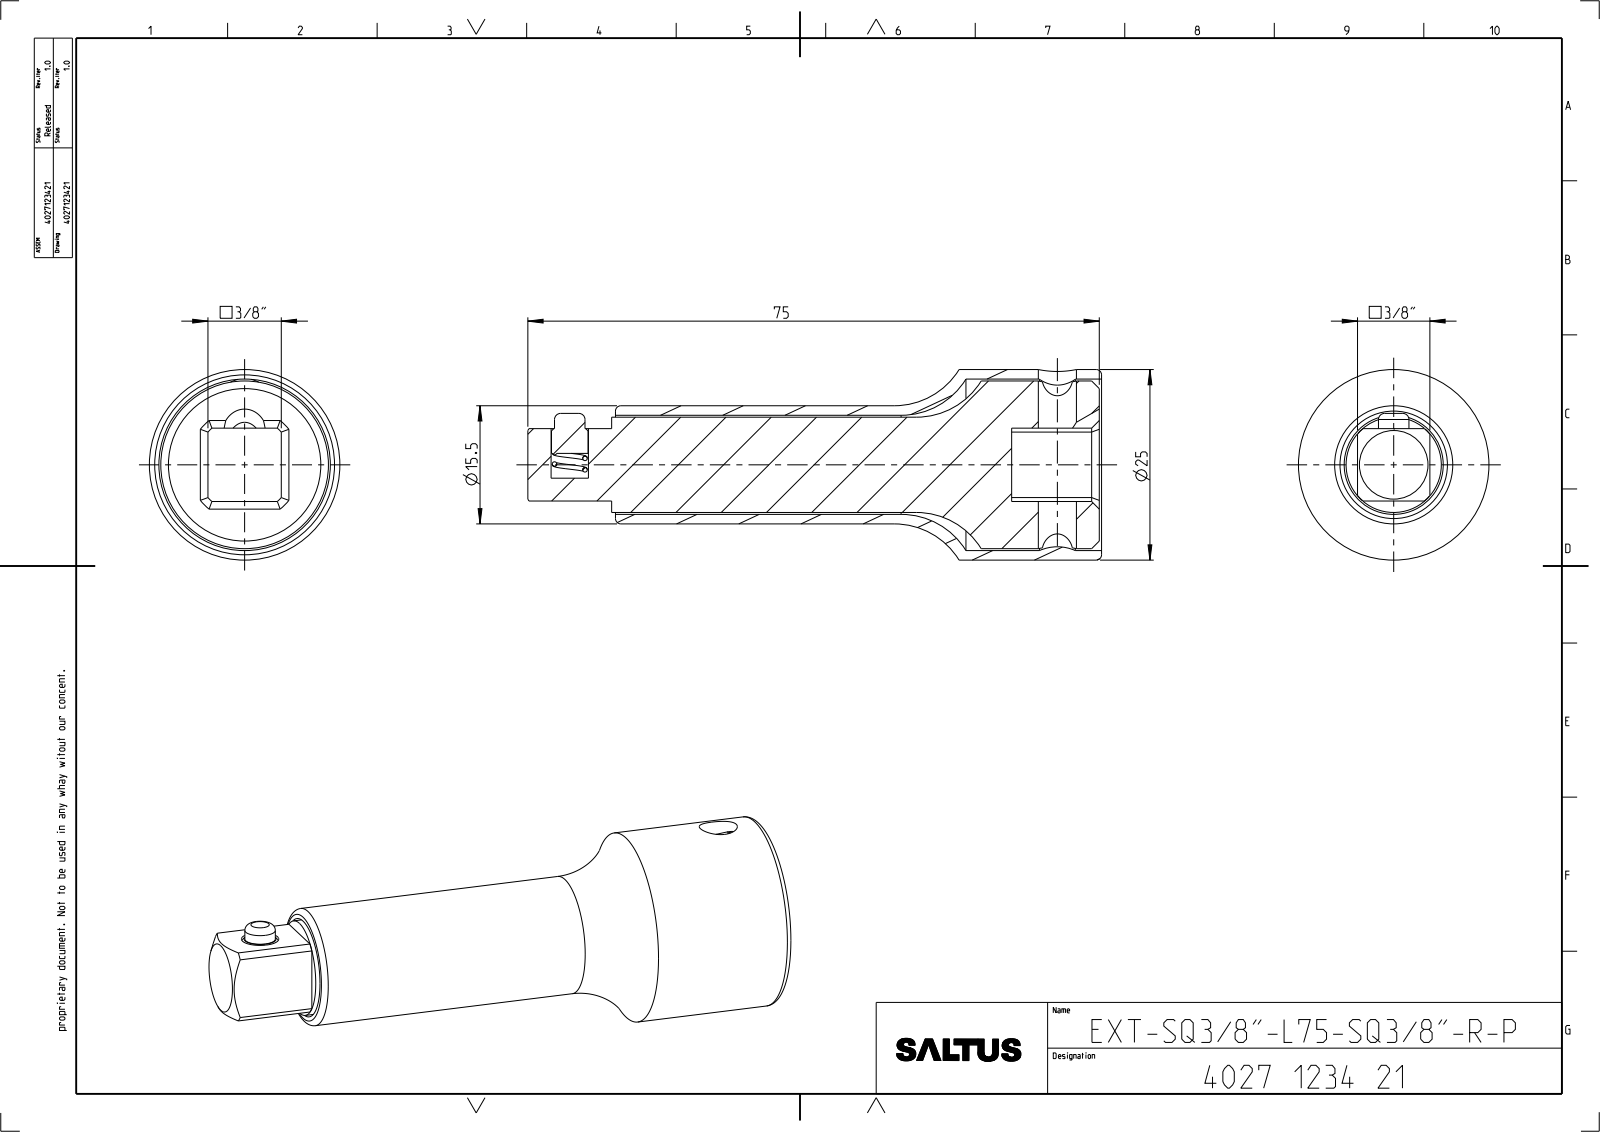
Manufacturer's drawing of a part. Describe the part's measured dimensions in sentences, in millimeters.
The part is named "4027123401; 4027038335; 4027123421_ASM". Its 3-D file was written by "CREO PARAMETRIC BY PTC INC, 2022414 (CONFIG_CONTROL_DESIGN)". It is 3 solids with 88 faces: 24 planar, 37 cylindrical and 27 other. Overall it measures 75.3 by 25 by 25 millimeters. Its volume is 16 383 cubic millimeters and its surface area 12 049 square millimeters. Round holes: 1 of diameter 4.9, 1 of diameter 5, 1 of diameter 13, 1 of diameter 22.5. Round bosses or shafts: 1 of diameter 25, 1 of diameter 22, 1 of diameter 15.5, 1 of diameter 12.5, 1 of diameter 4.8, 1 of diameter 4. Partial cylindrical surfaces (rounded edges, fillets, slot ends): 1 of radius 3, 1 of radius 6.22, 1 of radius 6.45. The main face-to-face distances are 9.56, 9.5, 9.62, 11.5, 63.5, 75, 11.8, 75.3, 64.3, 64. The hole center spacings are 64.
